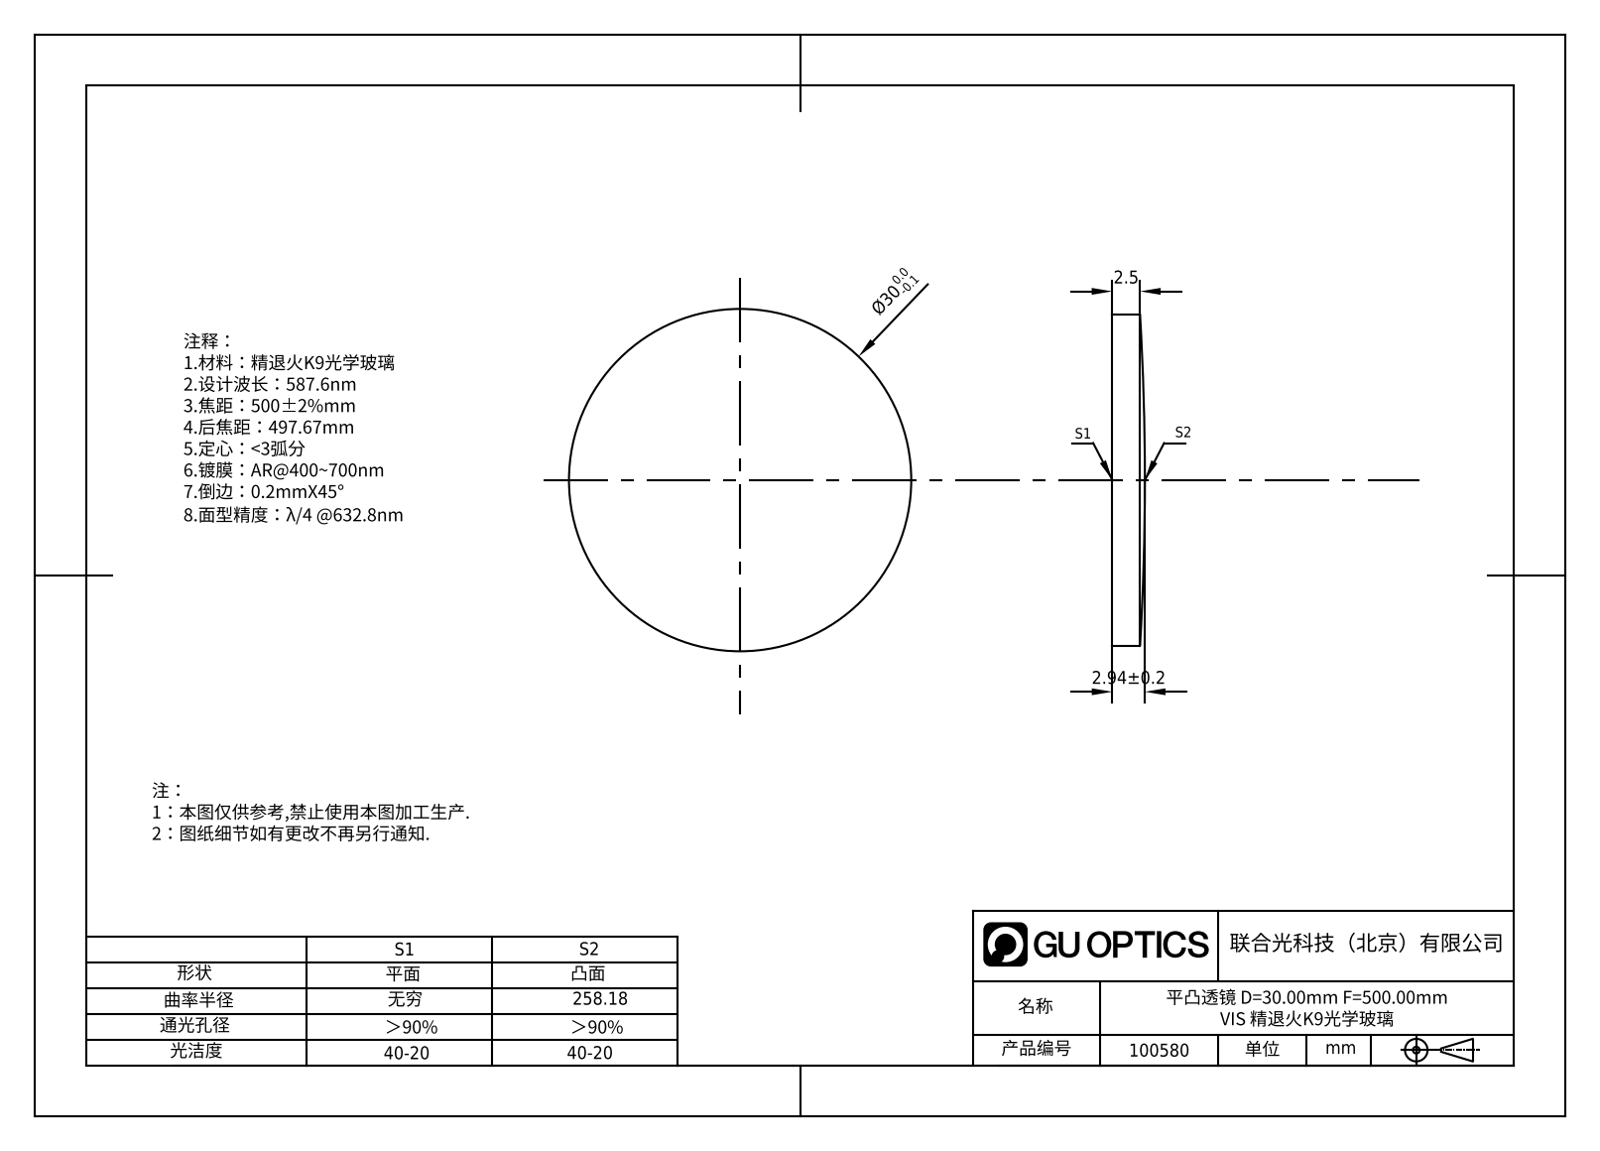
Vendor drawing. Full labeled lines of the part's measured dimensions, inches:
Part name (STEP PRODUCT): 100580
STEP written by: SolidWorks 2020 (CONFIG_CONTROL_DESIGN)
Units: inches
Bodies: 1 solid, 5 faces (1 planar, 2 cylindrical, 2 other)
Overall size (bounding box): 1.181 × 1.181 × 0.116
Volume: 0.117 in³ · Surface area: 2.558 in²
Round bosses / shafts (diameter × count): ⌀1.181 ×1
